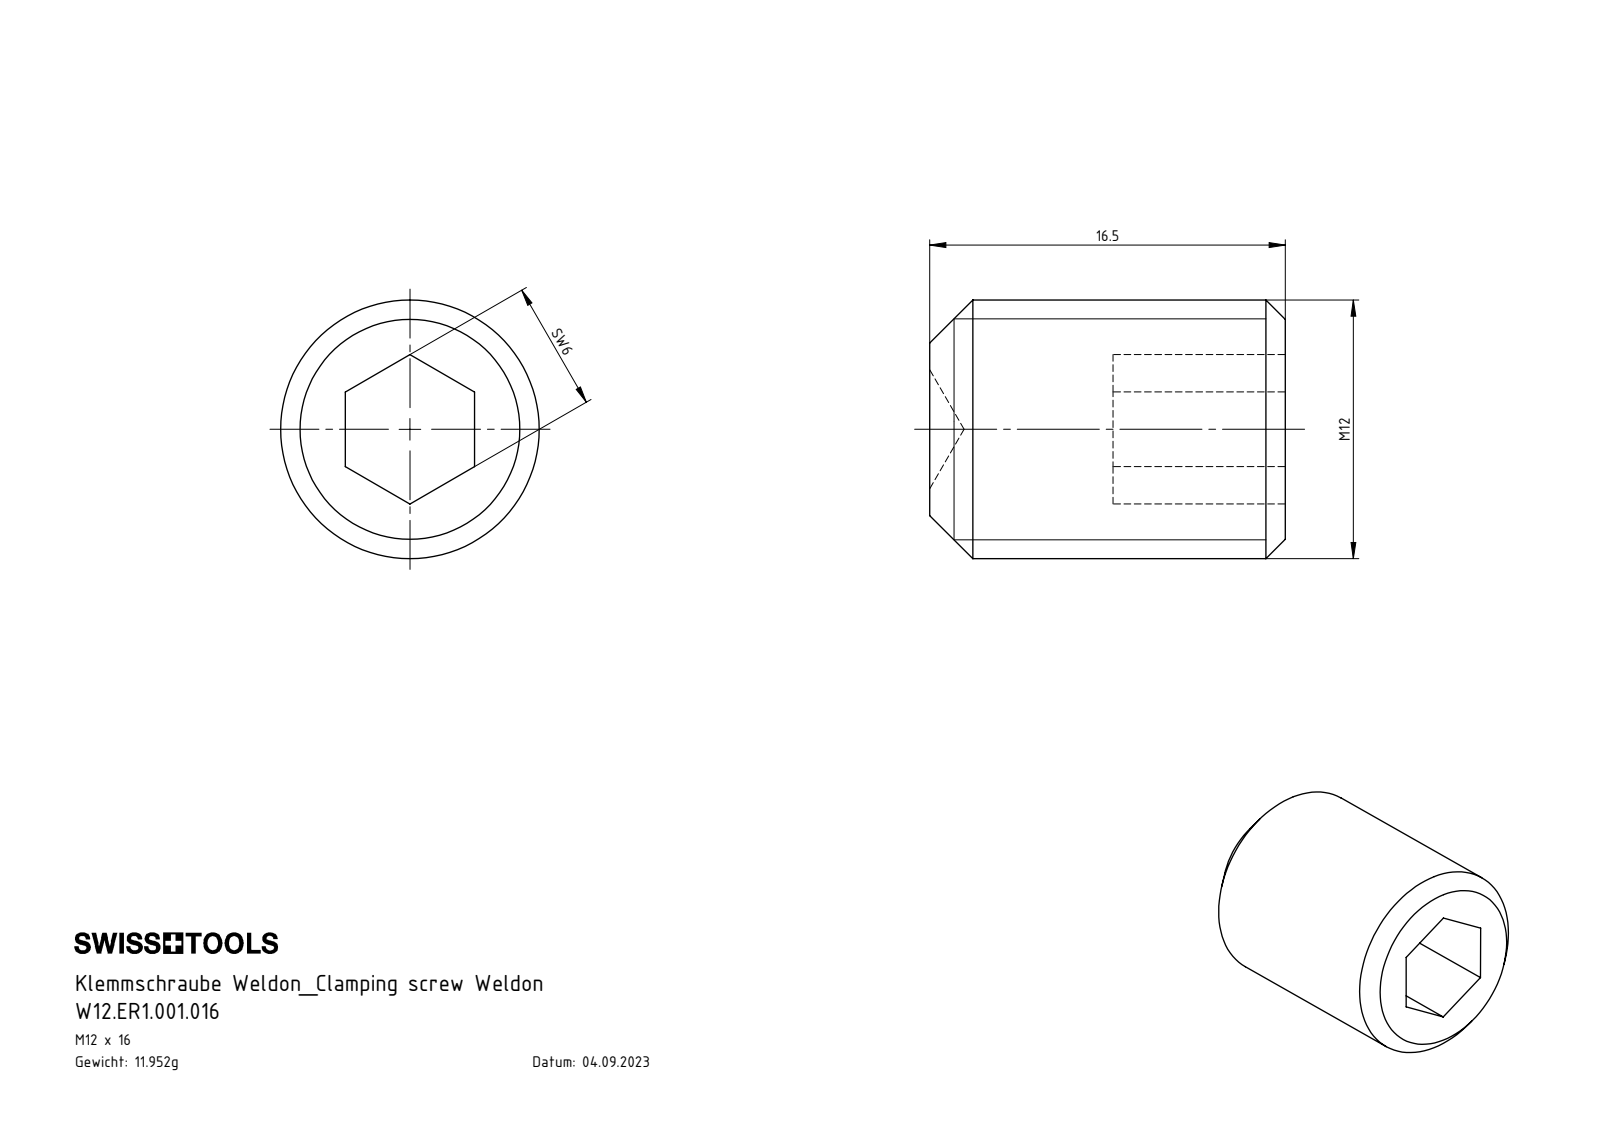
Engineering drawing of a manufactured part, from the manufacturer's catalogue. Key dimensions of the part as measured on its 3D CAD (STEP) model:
Part name (STEP PRODUCT): W12.ER1.001.016
STEP written by: SolidWorks 2017 (AUTOMOTIVE_DESIGN)
Units: millimetres
Bodies: 1 solid, 17 faces (9 planar, 2 cylindrical, 6 other)
Overall size (bounding box): 16.5 × 12 × 12
Volume: 1 523 mm³ · Surface area: 948 mm²
Round bosses / shafts (diameter × count): ⌀12 ×1
Main face-to-face distances: 6, 8, 16.5, 8.5
